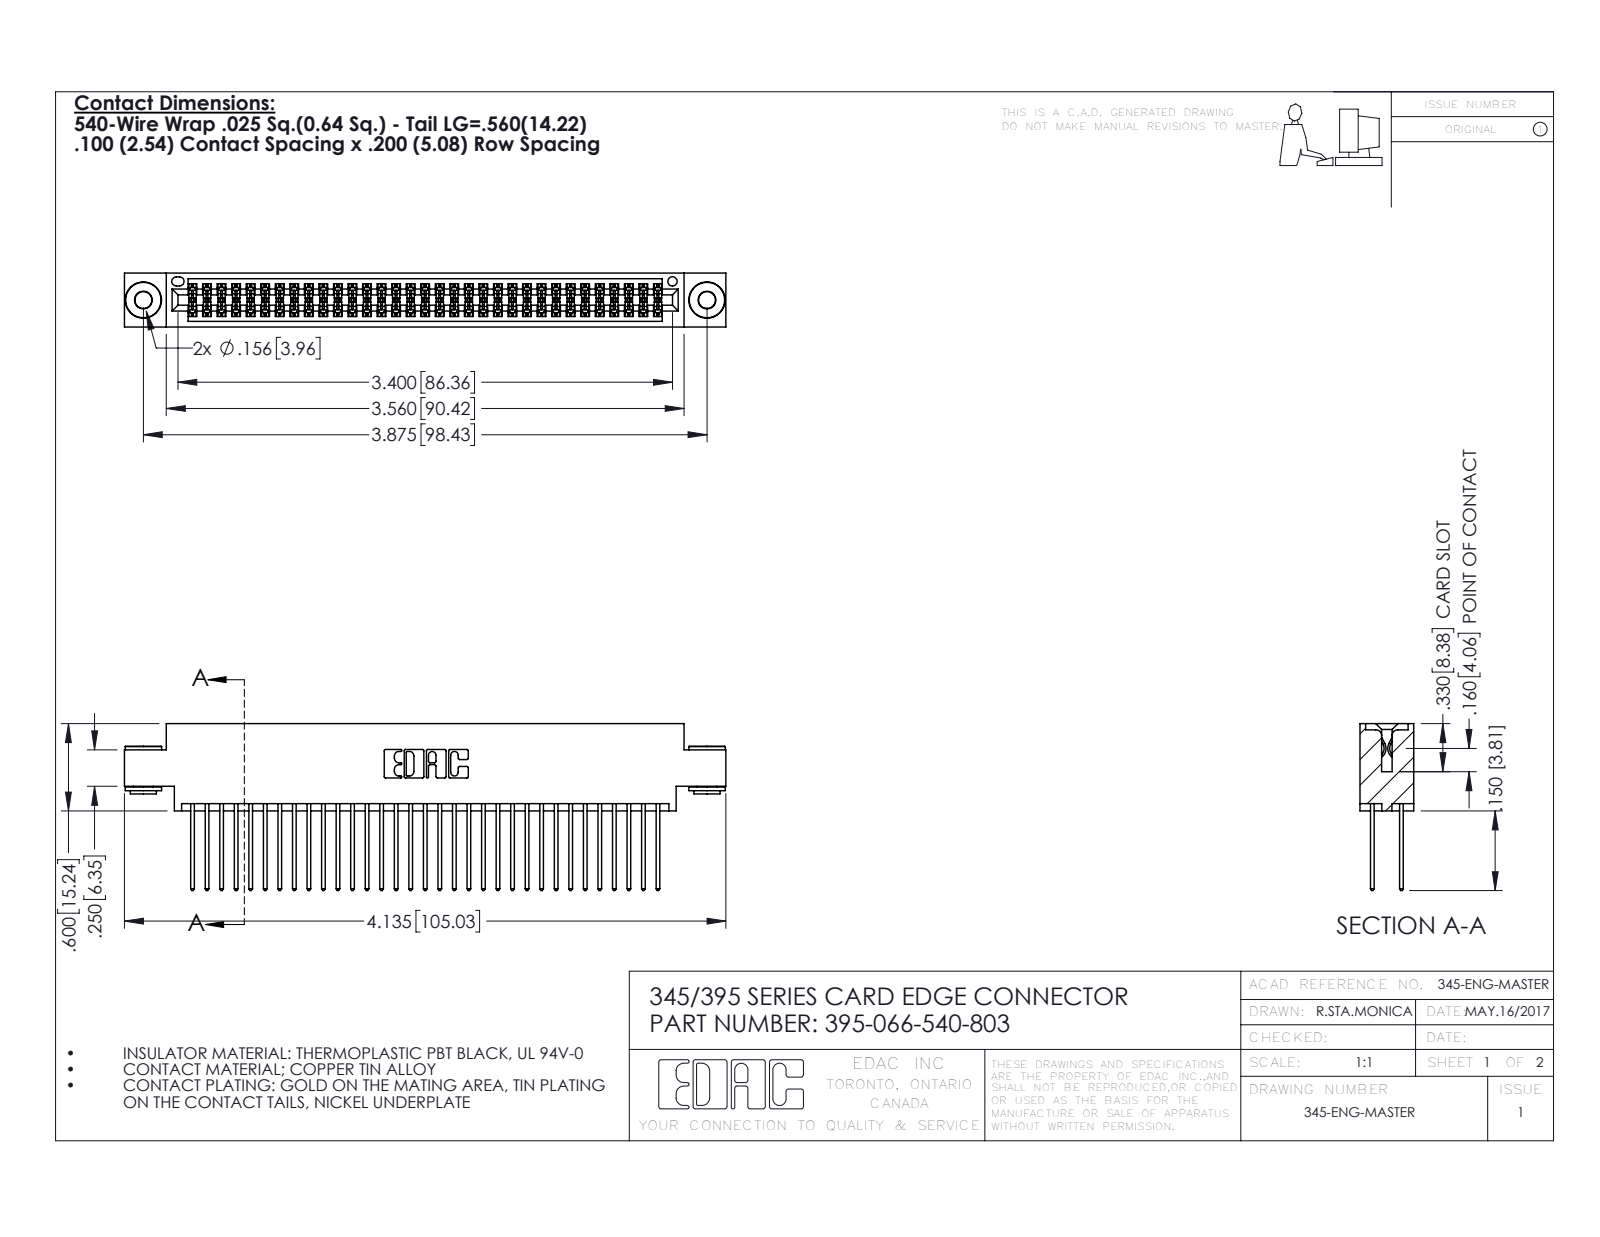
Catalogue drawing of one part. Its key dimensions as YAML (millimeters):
part_name: "395-066-540-803; 345 Part_0.170 Offset - 0.156 Dia-TH; 345-250-002_345-250-002-102; 345-292-001_345-293-140"
step_written_by: "SolidWorks 2016 (CONFIG_CONTROL_DESIGN)"
units: millimeters
bodies: {solids: 69, faces: 3468, planar: 2272, cylindrical: 1188, other: 8}
overall_size: [105, 29.1, 9.4]
volume: 10300
surface_area: 16520
round_holes:
  - {diameter: 2.9, count: 2}
  - {diameter: 4, count: 2}
  - {diameter: 1.6, count: 1}
round_bosses_or_shafts:
  - {diameter: 6.4, count: 2}
  - {diameter: 4.6, count: 2}
  - {diameter: 3.5, count: 2}
partial_cylinders:
  - {radius: 0.2, count: 99}
  - {radius: 0.3, count: 66}
  - {radius: 0.3, count: 22}
  - {radius: 0.2, count: 6}
  - {radius: 0.8, count: 6}
  - {radius: 0.7, count: 3}
  - {radius: 0.4, count: 2}
  - {radius: 0.5, count: 2}
face_to_face_distances: [1.8, 7.6, 5.1, 2.5, 6.9, 0.6, 9.4, 5.7, 4.4, 3.8]
hole_center_spacings: [6.9, 92.5, 98.4]
